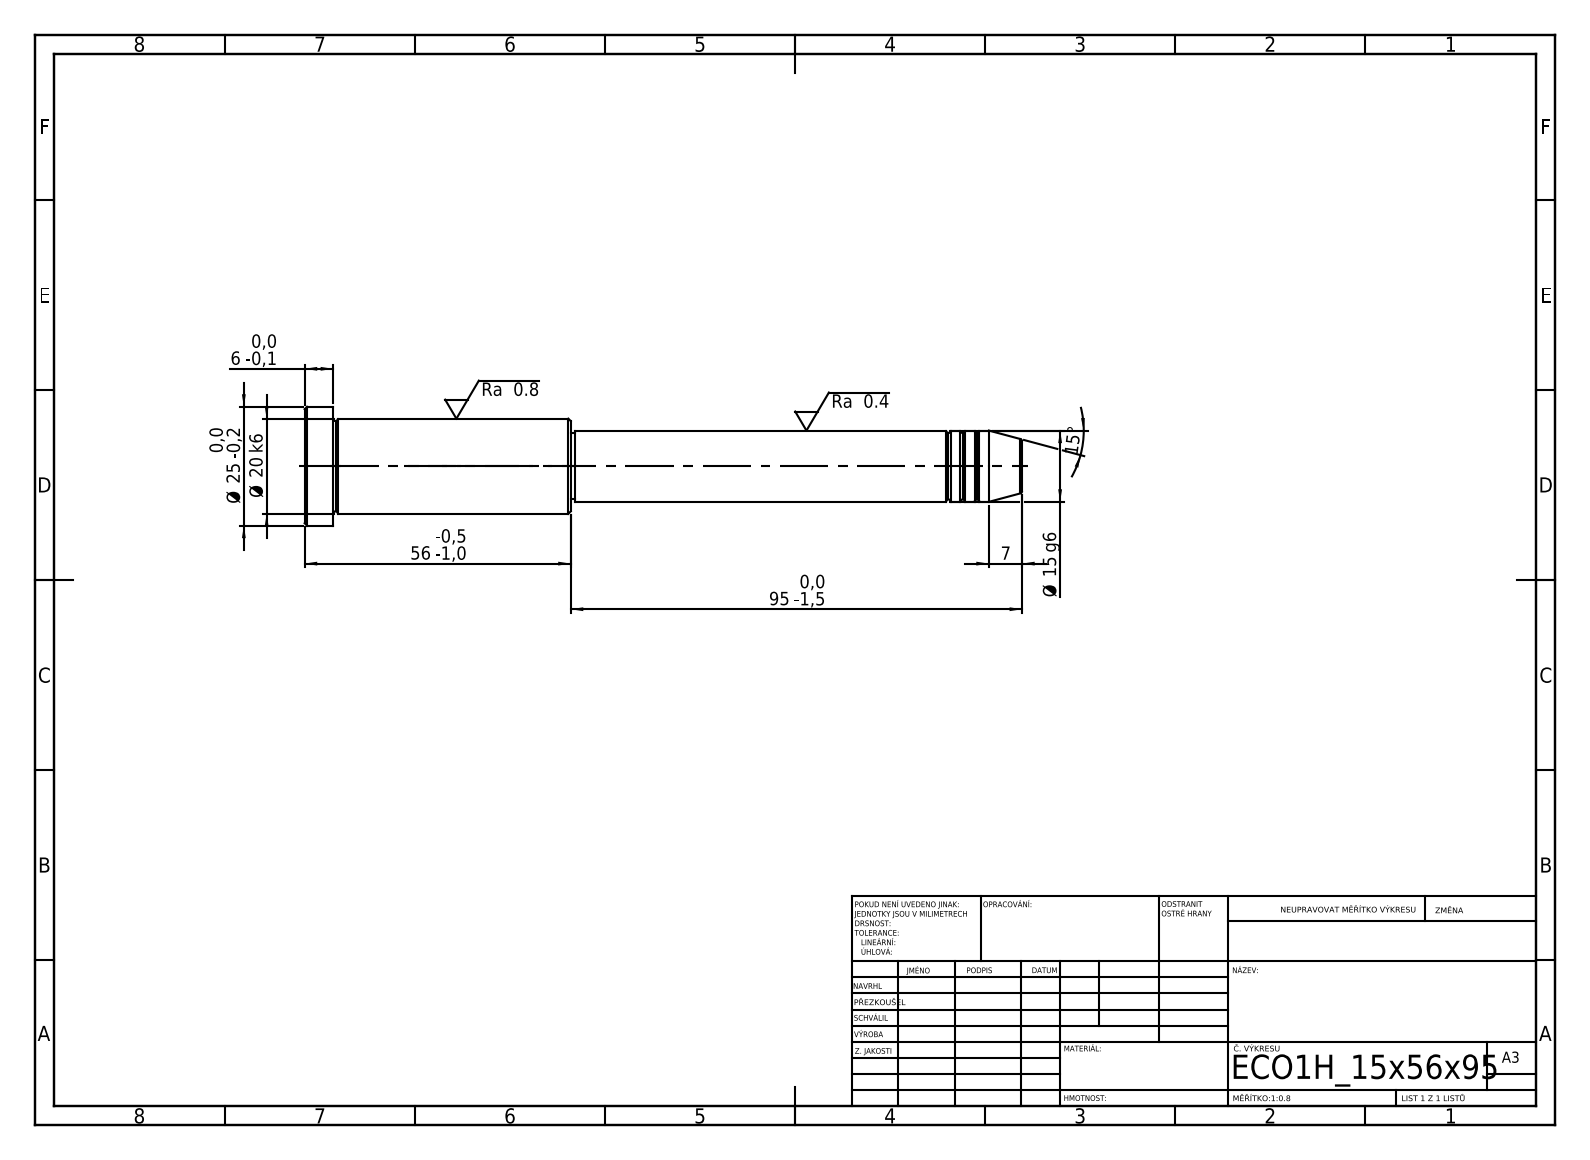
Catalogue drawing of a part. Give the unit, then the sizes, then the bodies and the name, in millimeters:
Units: millimetres
Overall size (bounding box): 151 × 25 × 25
Round bosses / shafts (diameter × count): ⌀25 ×1, ⌀20 ×1, ⌀15 ×1, ⌀14 ×1
Main face-to-face distances: 6, 50, 56, 95, 145, 151, 94, 1, 51, 57
Volume: 35 038 mm³ · Surface area: 9 063 mm²
Bodies: 1 solid, 43 faces (5 planar, 14 cylindrical, 24 other)
STEP written by: SolidWorks 2019 (CONFIG_CONTROL_DESIGN)
